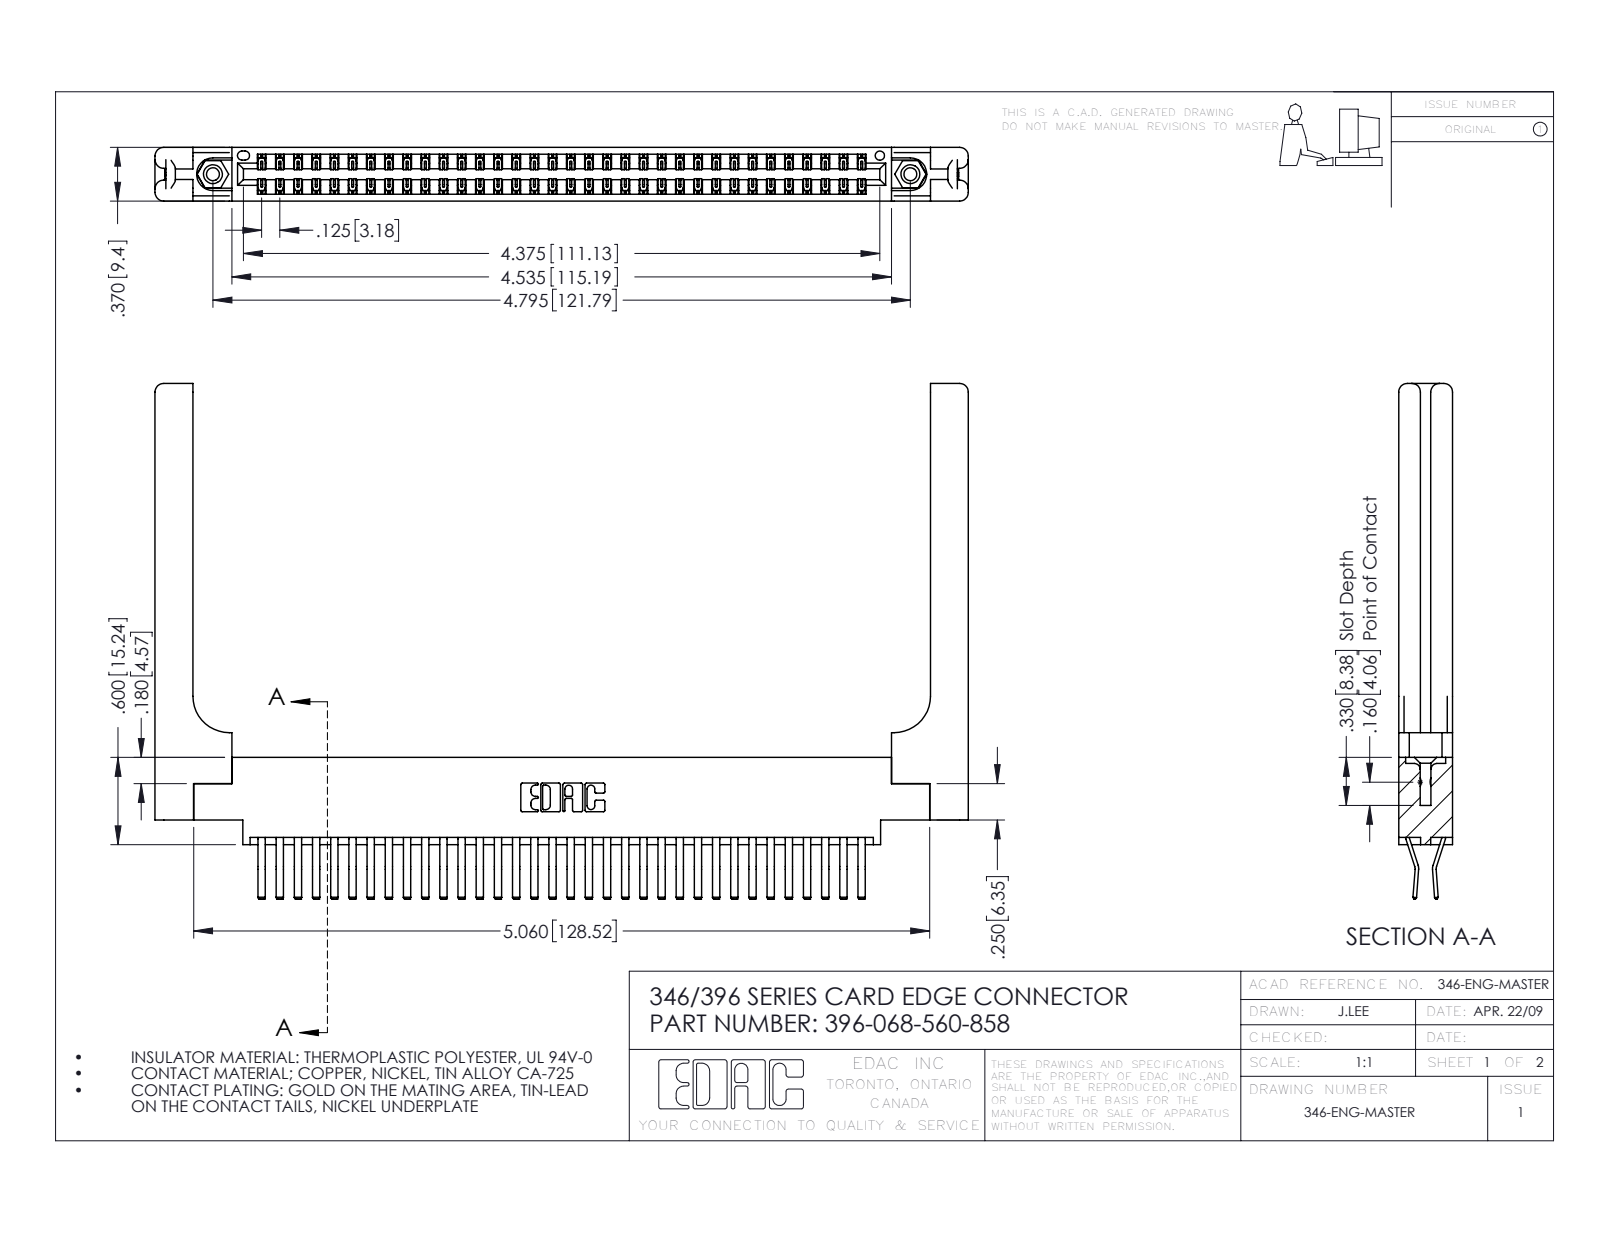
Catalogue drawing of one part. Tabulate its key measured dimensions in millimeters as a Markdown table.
| quantity | value |
| --- | --- |
| part name | 396-068-560-858; 345-292-001_560 Tail; 346 Part_0.170 Offset - 0.156 Dia-TH; 345-250-001_345-250-001-102 (+1 more) |
| STEP written by | SolidWorks 2016 (CONFIG_CONTROL_DESIGN) |
| units | millimeters |
| bodies | 73 solids, 4054 faces (2608 planar, 1386 cylindrical, 60 other) |
| overall size | 142 × 90 × 9.4 |
| volume | 21 570 mm³ |
| surface area | 25 570 mm² |
| round holes (diameter × count) | 2.3 × 2, 3.2 × 2, 4 × 2, 1.6 × 1 |
| round bosses / shafts (diameter × count) | 3.9 × 2 |
| partial cylindrical surfaces (radius × count) | 0.2 × 102, 0.3 × 22, 1.5 × 16, 0.2 × 6, 0.8 × 6, 0.7 × 3, 0.3 × 2, 0.4 × 2 |
| main face-to-face distances | 9.4, 1.2, 8.2, 1.8, 3.8, 3.8, 0.6, 6.4, 7.6, 7 |
| hole center spacings | 6.2, 116.5, 121.8 |
